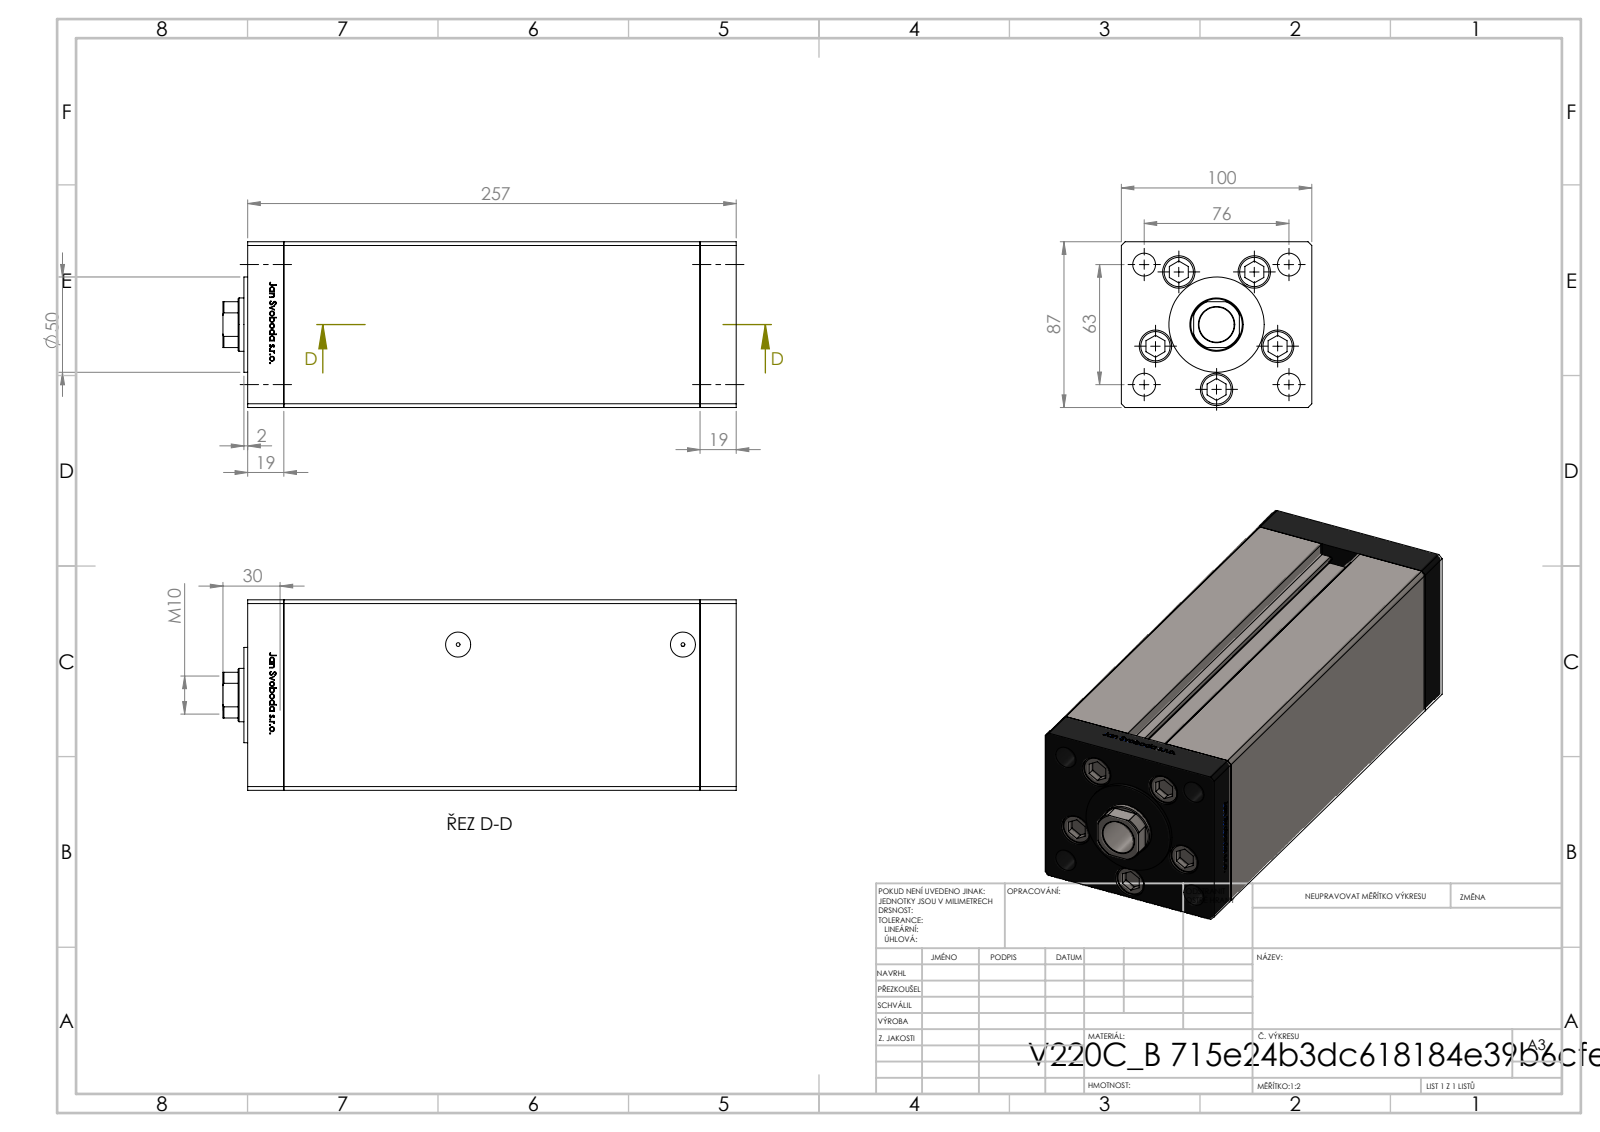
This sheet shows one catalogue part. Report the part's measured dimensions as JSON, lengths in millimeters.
{"part_name": "V220C_FRONT_B; ALLEN BOLT; V220C_B MIDDLE; V220C BACK_B (+1 more)", "step_written_by": "SolidWorks 2019 (CONFIG_CONTROL_DESIGN)", "units": "millimeters", "bodies": {"solids": 14, "faces": 1185, "planar": 464, "cylindrical": 147, "other": 574}, "overall_size": [269.5, 100, 87], "volume_mm3": 1933000, "surface_area_mm2": 250047, "round_holes": [[13.5, 7], [17, 5], [12, 4], [2, 2], [13.16, 2], [18.5, 1], [28, 1]], "round_bosses_or_shafts": [[8, 5], [17, 2], [50, 1]], "partial_cylinders_radius": [[0.93, 2], [13.5, 1]], "face_to_face_distances": [100, 87, 19, 218.5, 237.5, 34.25, 256.5, 15.25, 203.25, 222.25], "hole_center_spacings": [34, 18.59, 39.64, 49.36, 57.95, 21.03, 38.08, 39.27]}
